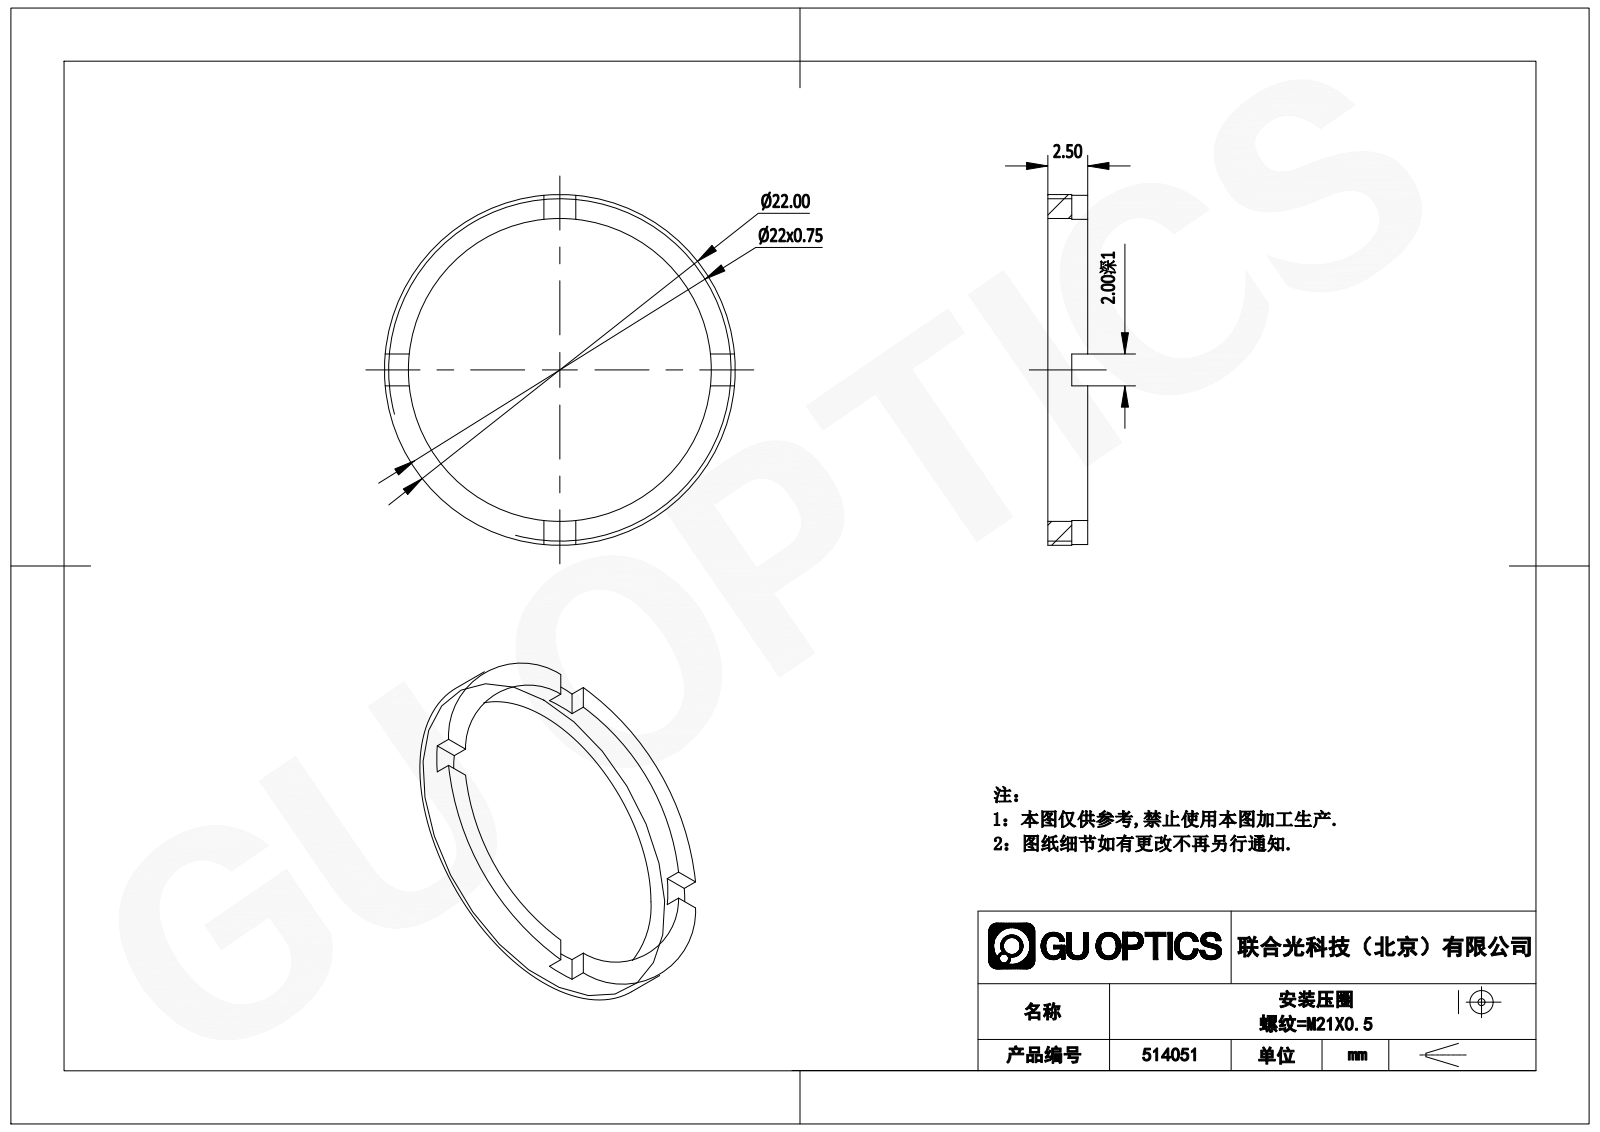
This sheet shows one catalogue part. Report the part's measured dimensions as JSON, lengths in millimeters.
{"part_name": "514051", "step_written_by": "SolidWorks 2020 (CONFIG_CONTROL_DESIGN)", "units": "millimeters", "bodies": {"solids": 1, "faces": 21, "planar": 17, "cylindrical": 4, "other": 0}, "overall_size": [22, 22, 2.5], "volume_mm3": 229, "surface_area_mm2": 511, "round_holes": [[19, 1]], "round_bosses_or_shafts": [[22, 1]], "face_to_face_distances": [2.5, 1.5, 1, 2]}
